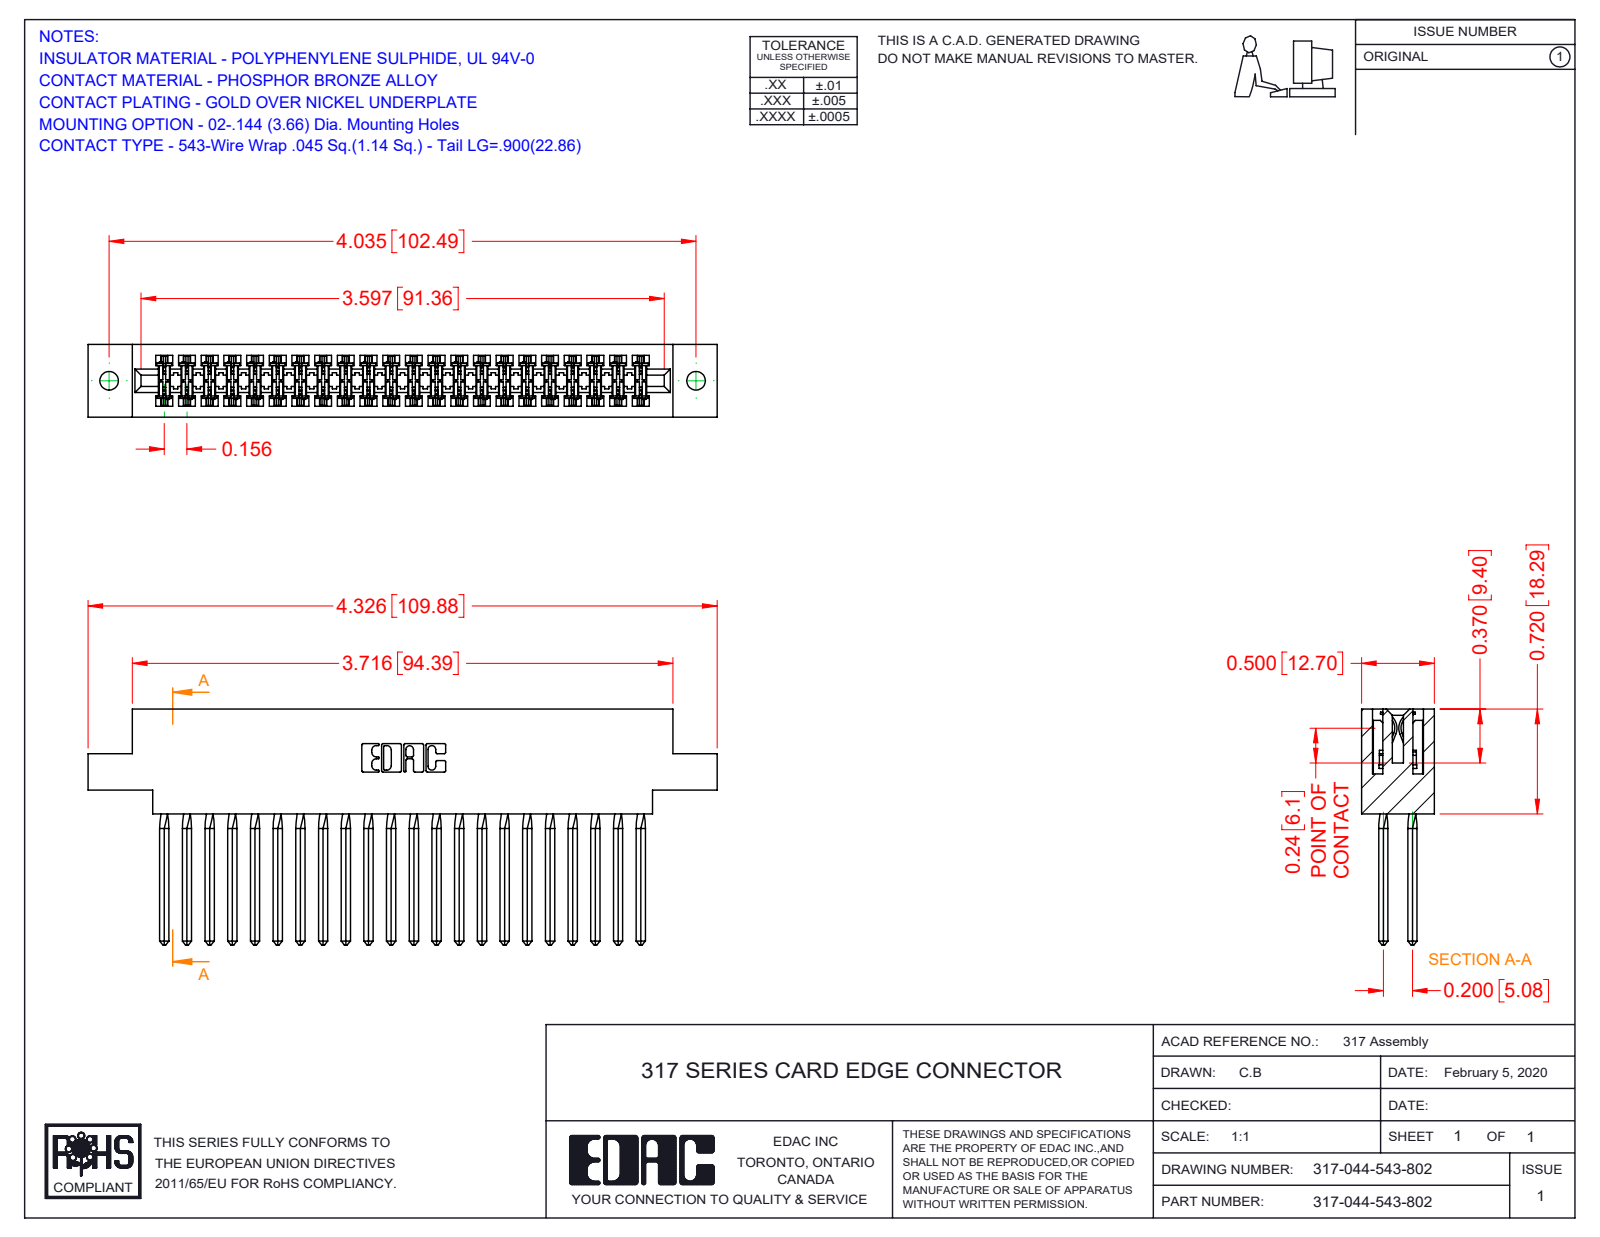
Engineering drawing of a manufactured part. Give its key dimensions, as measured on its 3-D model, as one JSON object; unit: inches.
{"part_name": "317 Part_.144 Dia; 317-044-543-802; 317-290-001_543", "step_written_by": "SolidWorks 2016 (CONFIG_CONTROL_DESIGN)", "units": "inches", "bodies": {"solids": 45, "faces": 4018, "planar": 3270, "cylindrical": 572, "other": 176}, "overall_size": [4.326, 1.62, 0.5], "volume_in3": 1.095, "surface_area_in2": 40.58, "round_holes": [[0.128, 2]], "partial_cylinders_radius": [[0.015, 88], [0.01, 22], [0.007, 6], [0.031, 6], [0.026, 3], [0.095, 2], [0.1, 2], [0.11, 2]], "face_to_face_distances": [0.5, 0.075, 0.425, 0.11, 0.35, 0.22, 0.195, 0.72, 0.094, 0.2], "hole_center_spacings": [4.035]}
